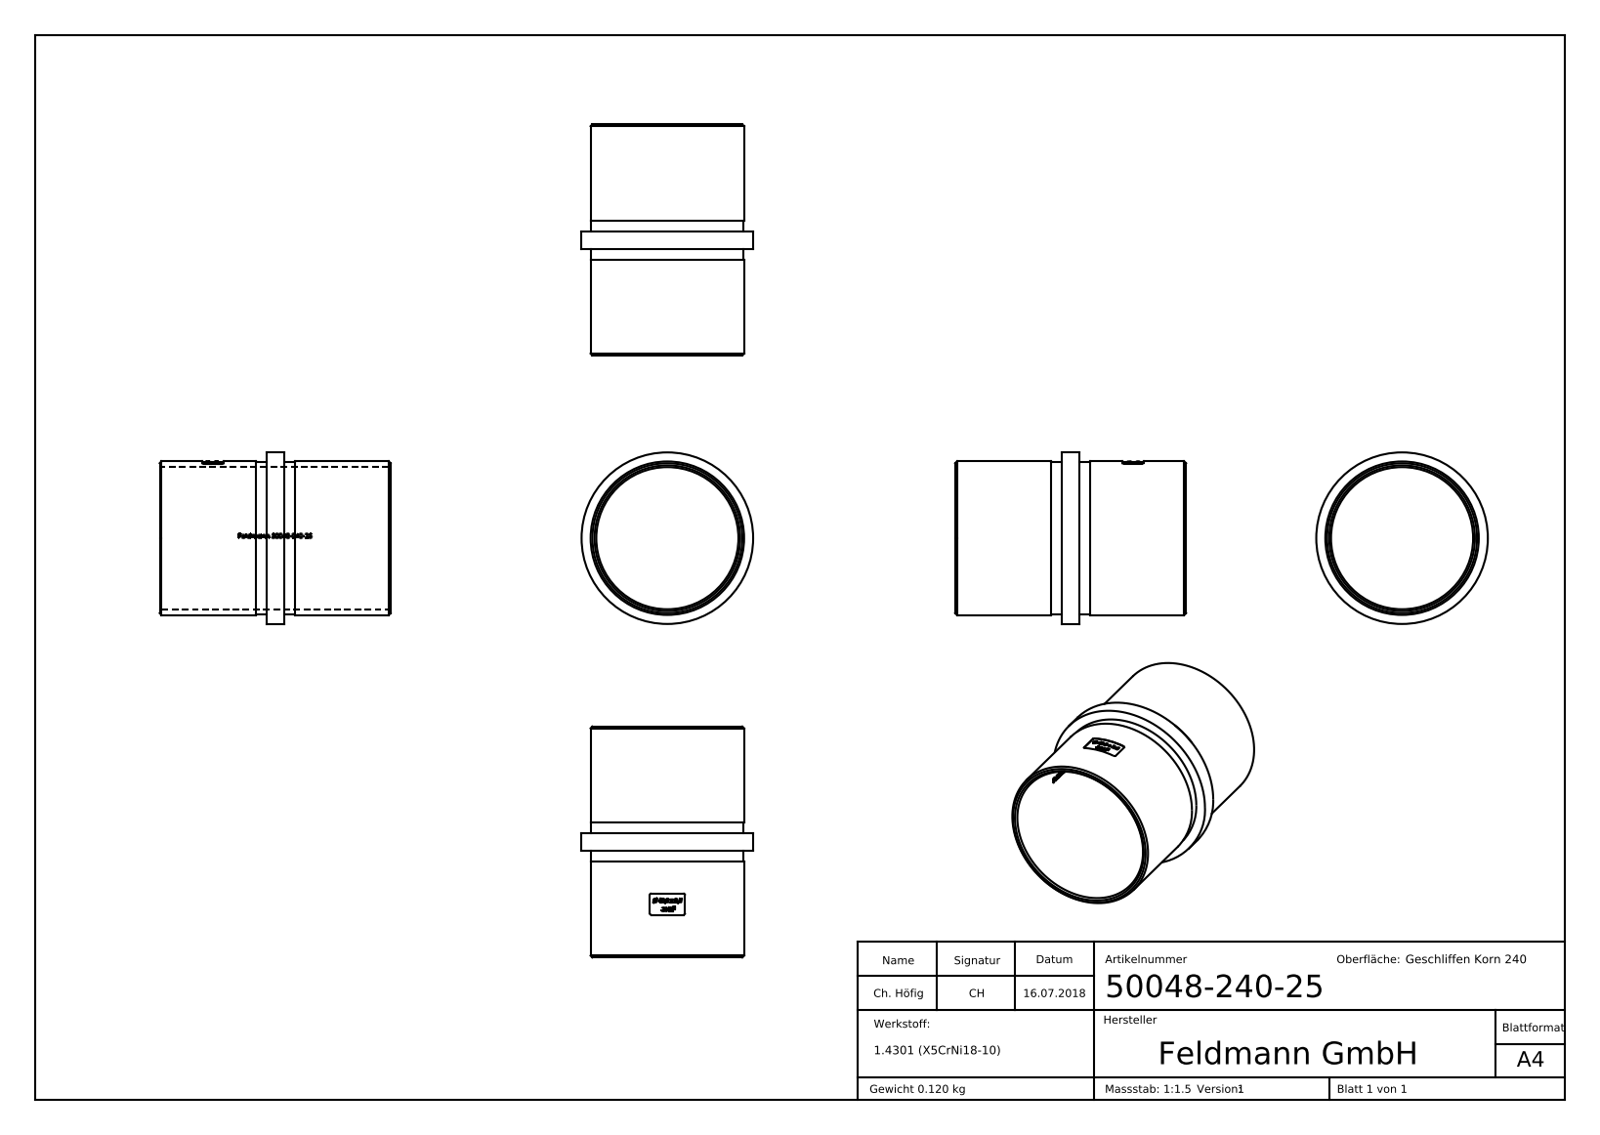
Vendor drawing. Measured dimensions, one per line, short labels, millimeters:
name: 50048-240-25
written by: SolidWorks 2015 (CONFIG_CONTROL_DESIGN)
unit: mm
bodies: 1 solid, 489 faces (208 planar, 73 cylindrical, 208 other)
size: 65 × 48.3 × 48.3
volume: 15 190 mm³; area: 18 189 mm²
holes: 1× ⌀40
bosses: 1× ⌀48.3, 1× ⌀43.2, 1× ⌀42.8
rounds: 4× R0.5, 1× R20.1, 1× R21.5
face distances: 5, 30, 35, 65, 27, 38, 3, 8, 11, 12
